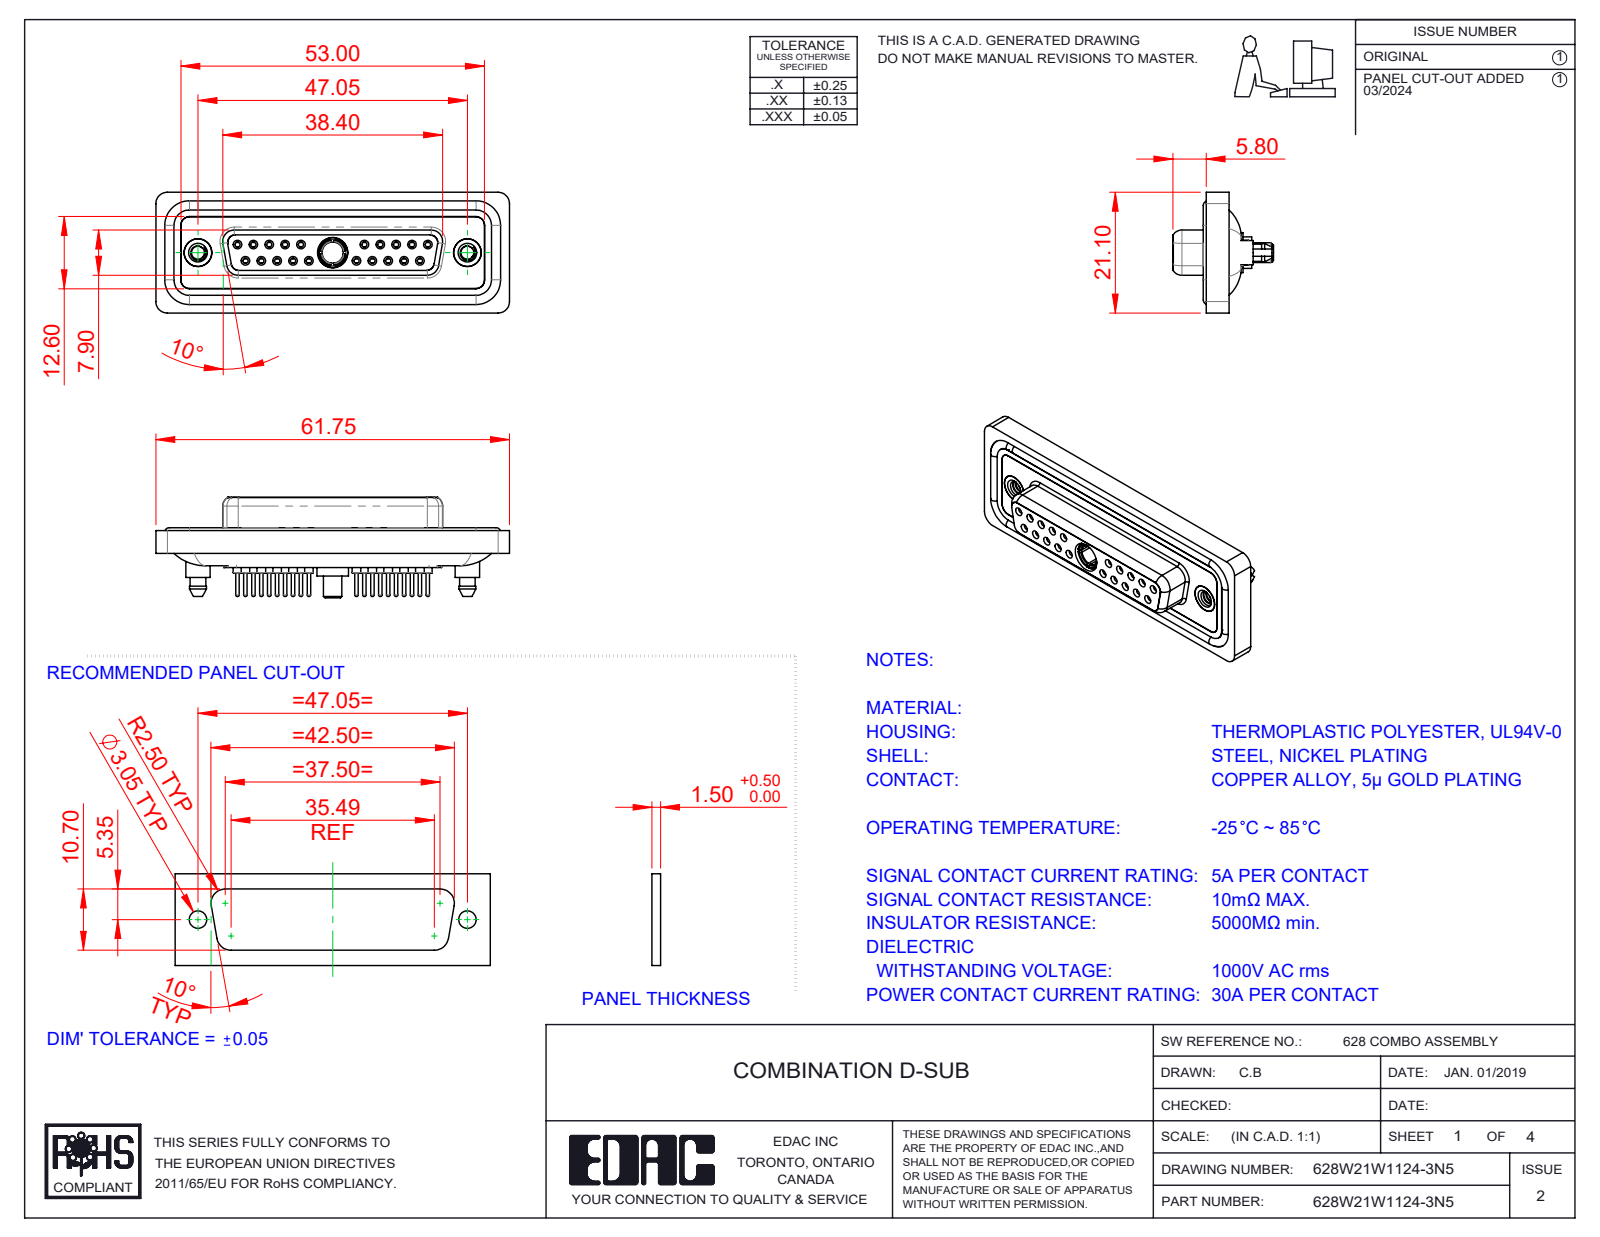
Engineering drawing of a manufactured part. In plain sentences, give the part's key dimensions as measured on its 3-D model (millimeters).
The part is named "628Combo Contact Row 1_24; 628Combo Housing_21W1; Power Socket_30A S; 628Combo Shell Front_25 Contacts (+5 more)". Its 3-D file was written by "SolidWorks 2023 (CONFIG_CONTROL_DESIGN)". It is 29 solids with 1610 faces: 450 planar, 623 cylindrical and 537 other. Overall it measures 61.75 by 21.1 by 17.55 millimeters. Its volume is 8 515 cubic millimeters and its surface area 14 340 square millimeters. Round holes: 20 of diameter 0.9, 20 of diameter 1.1, 20 of diameter 1.5, 20 of diameter 2, 10 of diameter 1.6, 10 of diameter 1.7, 3 of diameter 4.85, 2 of diameter 2.26, 2 of diameter 4, 2 of diameter 4.05, 2 of diameter 5, 1 of diameter 3.7. Round bosses or shafts: 20 of diameter 2.2, 20 of diameter 0.6, 14 of diameter 1.6, 2 of diameter 5.4, 2 of diameter 4.95, 2 of diameter 4.8, 2 of diameter 4.25, 1 of diameter 5.5. Partial cylindrical surfaces (rounded edges, fillets, slot ends): 24 of radius 1.5, 18 of radius 2, 10 of radius 1.6, 8 of radius 1.35, 4 of radius 0.25, 4 of radius 0.5, 4 of radius 0.6, 4 of radius 0.65. The main face-to-face distances are 0.4, 1.8, 7.45, 6.6, 5.65, 1.6, 0.5, 7.05, 2.9, 1.1. The hole center spacings are 3.16, 2.77, 5.54, 5.03, 8.31, 7.48, 16.62, 19.39.
